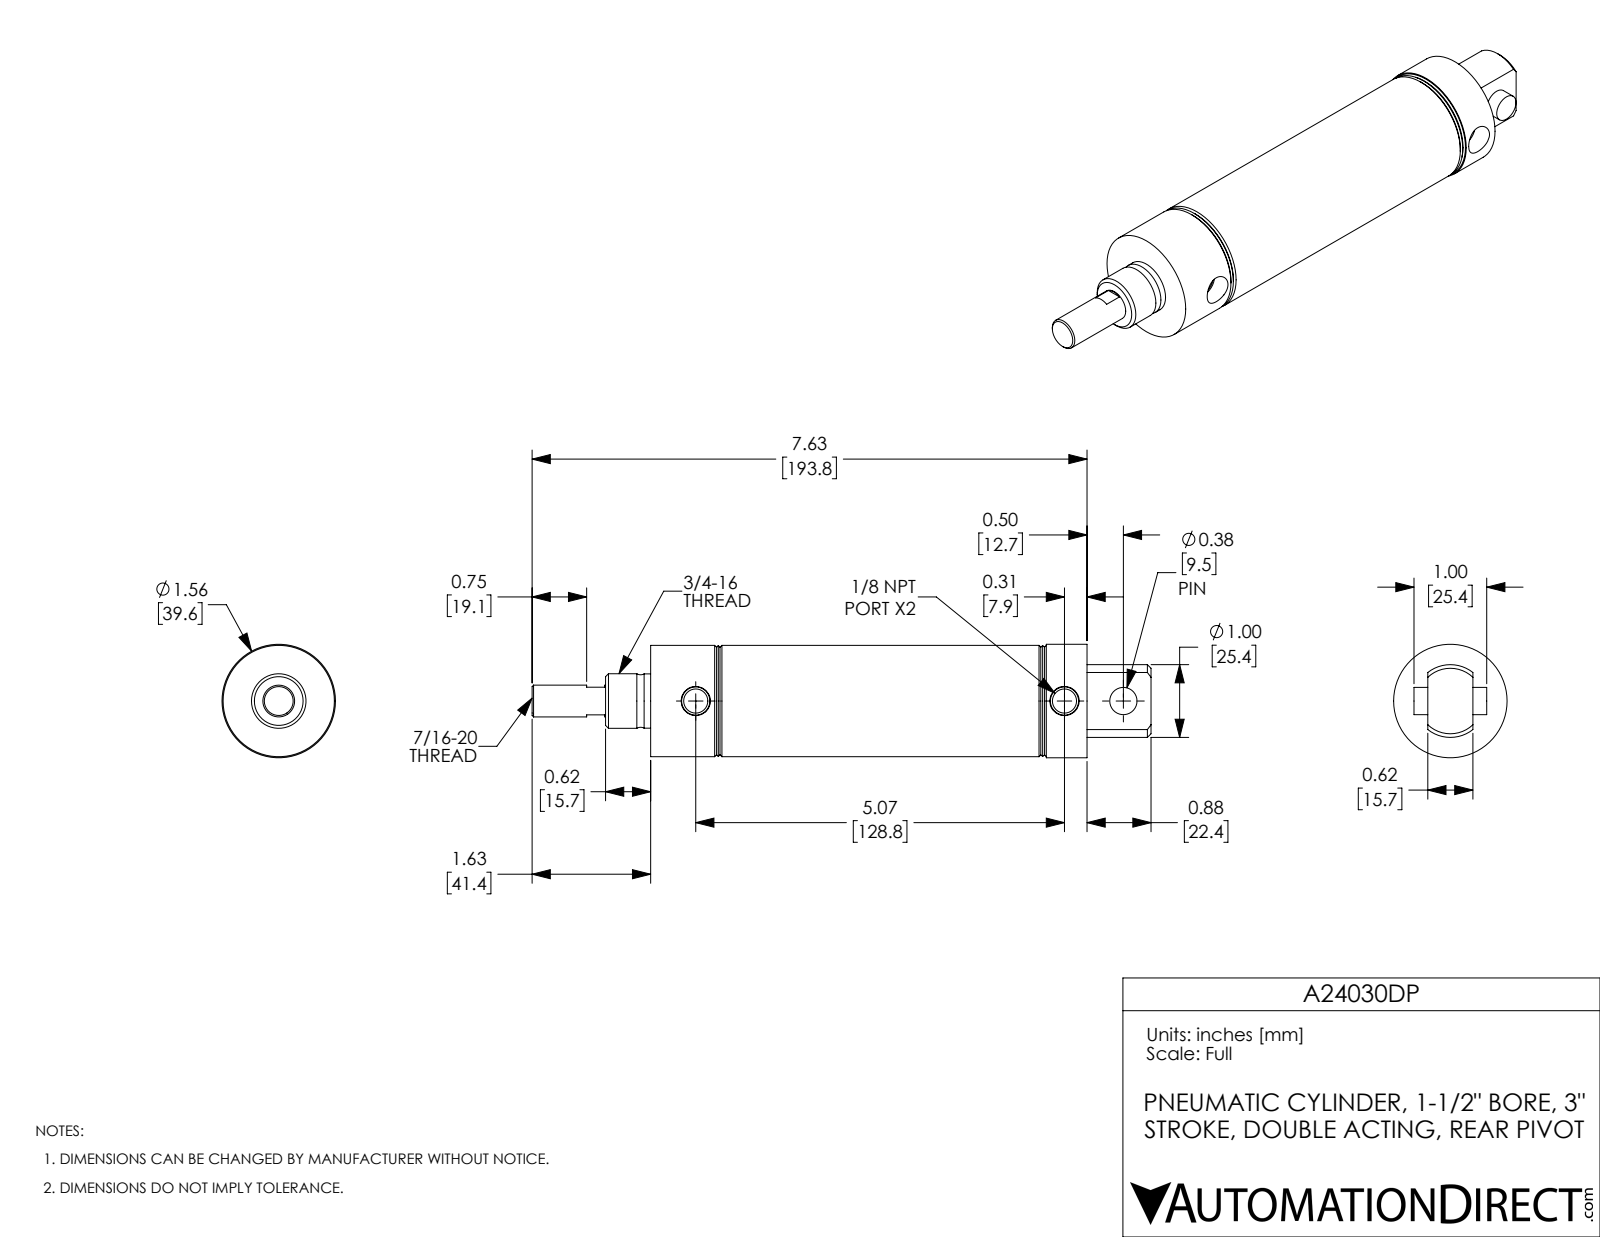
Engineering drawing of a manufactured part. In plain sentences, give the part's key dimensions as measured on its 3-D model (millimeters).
The part is named "A24030DP-Pin; A24030DP-Rod; A24030DP; A24030DP-MainBody". Its 3-D file was written by "SolidWorks 2017 (AUTOMOTIVE_DESIGN)". It is 3 solids with 84 faces: 22 planar, 28 cylindrical and 34 other. Overall it measures 216.2 by 39.6 by 39.6 millimeters. Its volume is 115 900 cubic millimeters and its surface area 49 140 square millimeters. Round holes: 2 of diameter 8.4, 1 of diameter 9.5, 1 of diameter 11.1, 1 of diameter 38.1. Round bosses or shafts: 1 of diameter 39.6, 1 of diameter 38.9, 1 of diameter 19.1, 1 of diameter 18.9. Partial cylindrical surfaces (rounded edges, fillets, slot ends): 1 of radius 12.7. The main face-to-face distances are 31.8, 120.7, 12.7, 88.9, 76.2, 108, 44.5, 152.4, 15.7, 22.4. The hole center spacings are 20.6, 128.8, 149.4.
